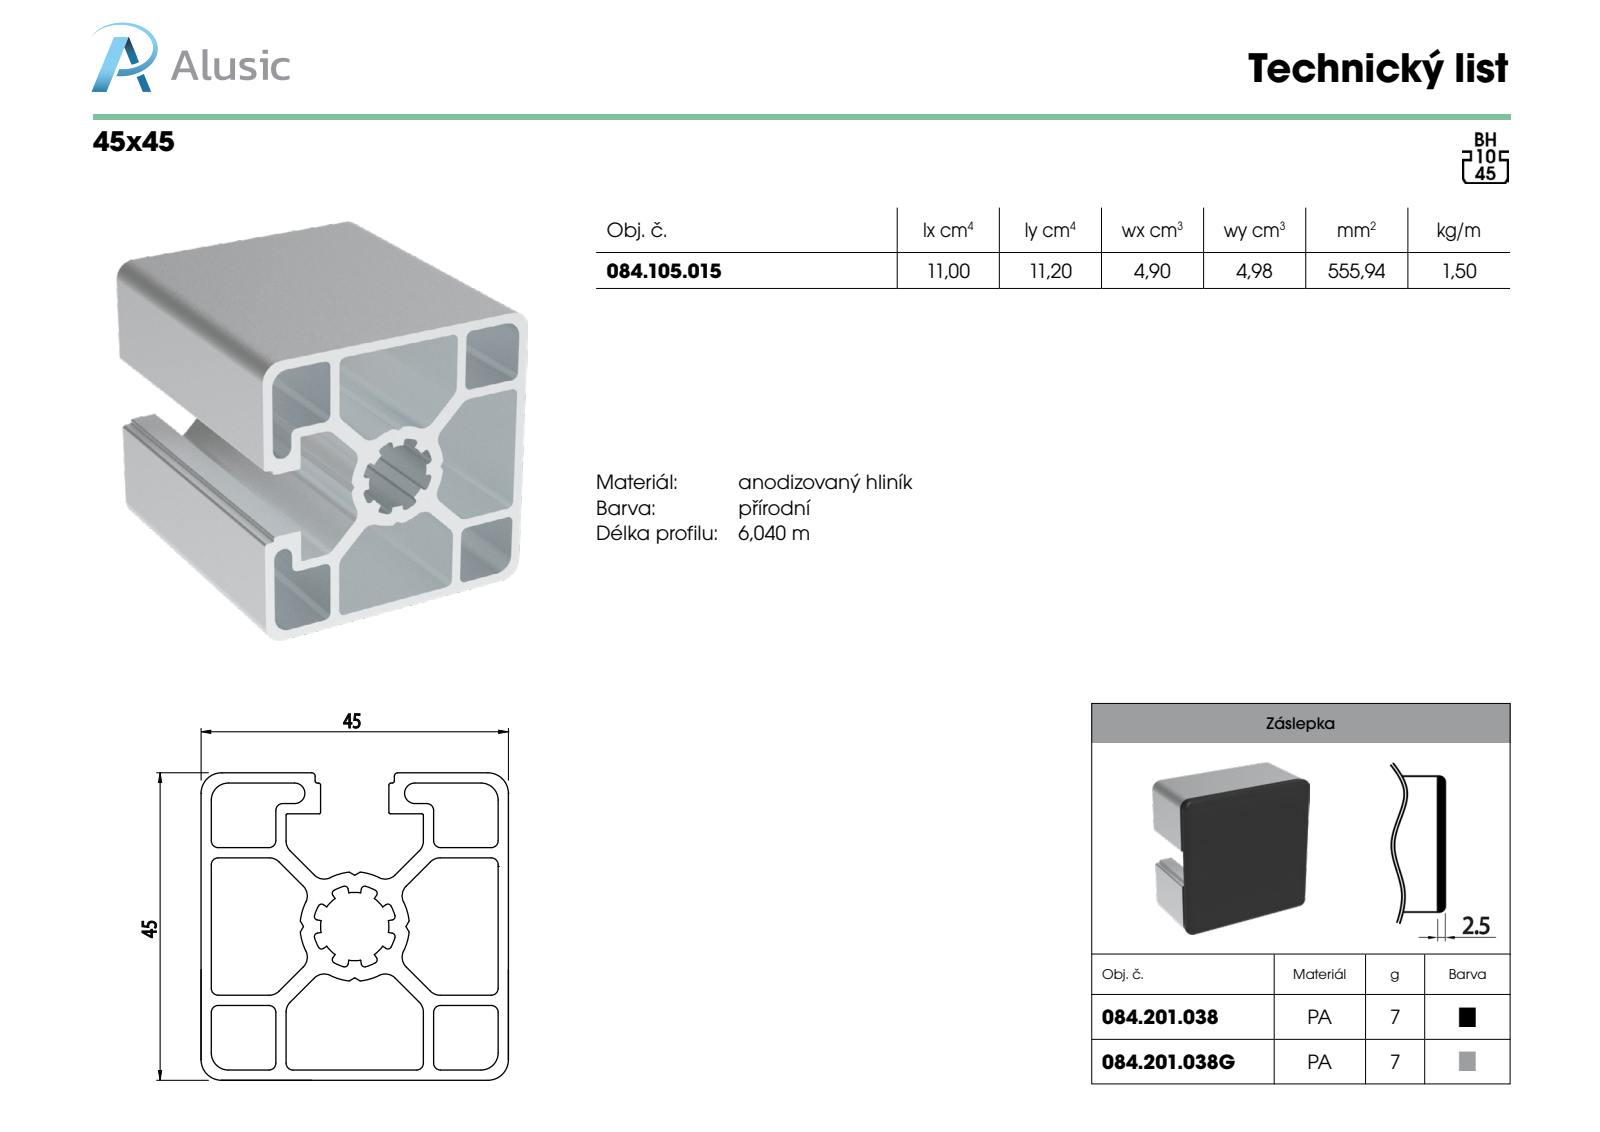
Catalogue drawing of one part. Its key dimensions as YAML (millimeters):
part_name: "084.105.015"
step_written_by: "SolidWorks 2018 (AUTOMOTIVE_DESIGN)"
units: millimeters
bodies: {solids: 1, faces: 177, planar: 76, cylindrical: 101, other: 0}
overall_size: [100, 45, 45]
volume: 55594
surface_area: 62236
partial_cylinders:
  - {radius: 0.5, count: 18}
  - {radius: 1, count: 18}
  - {radius: 2, count: 16}
  - {radius: 0.2, count: 4}
  - {radius: 0.3, count: 4}
  - {radius: 2.5, count: 4}
  - {radius: 3, count: 4}
  - {radius: 1.5, count: 2}
face_to_face_distances: [1.5, 43.5, 32.55, 10.95, 45, 34.05, 9.45, 12.45, 31.05, 21.6]
